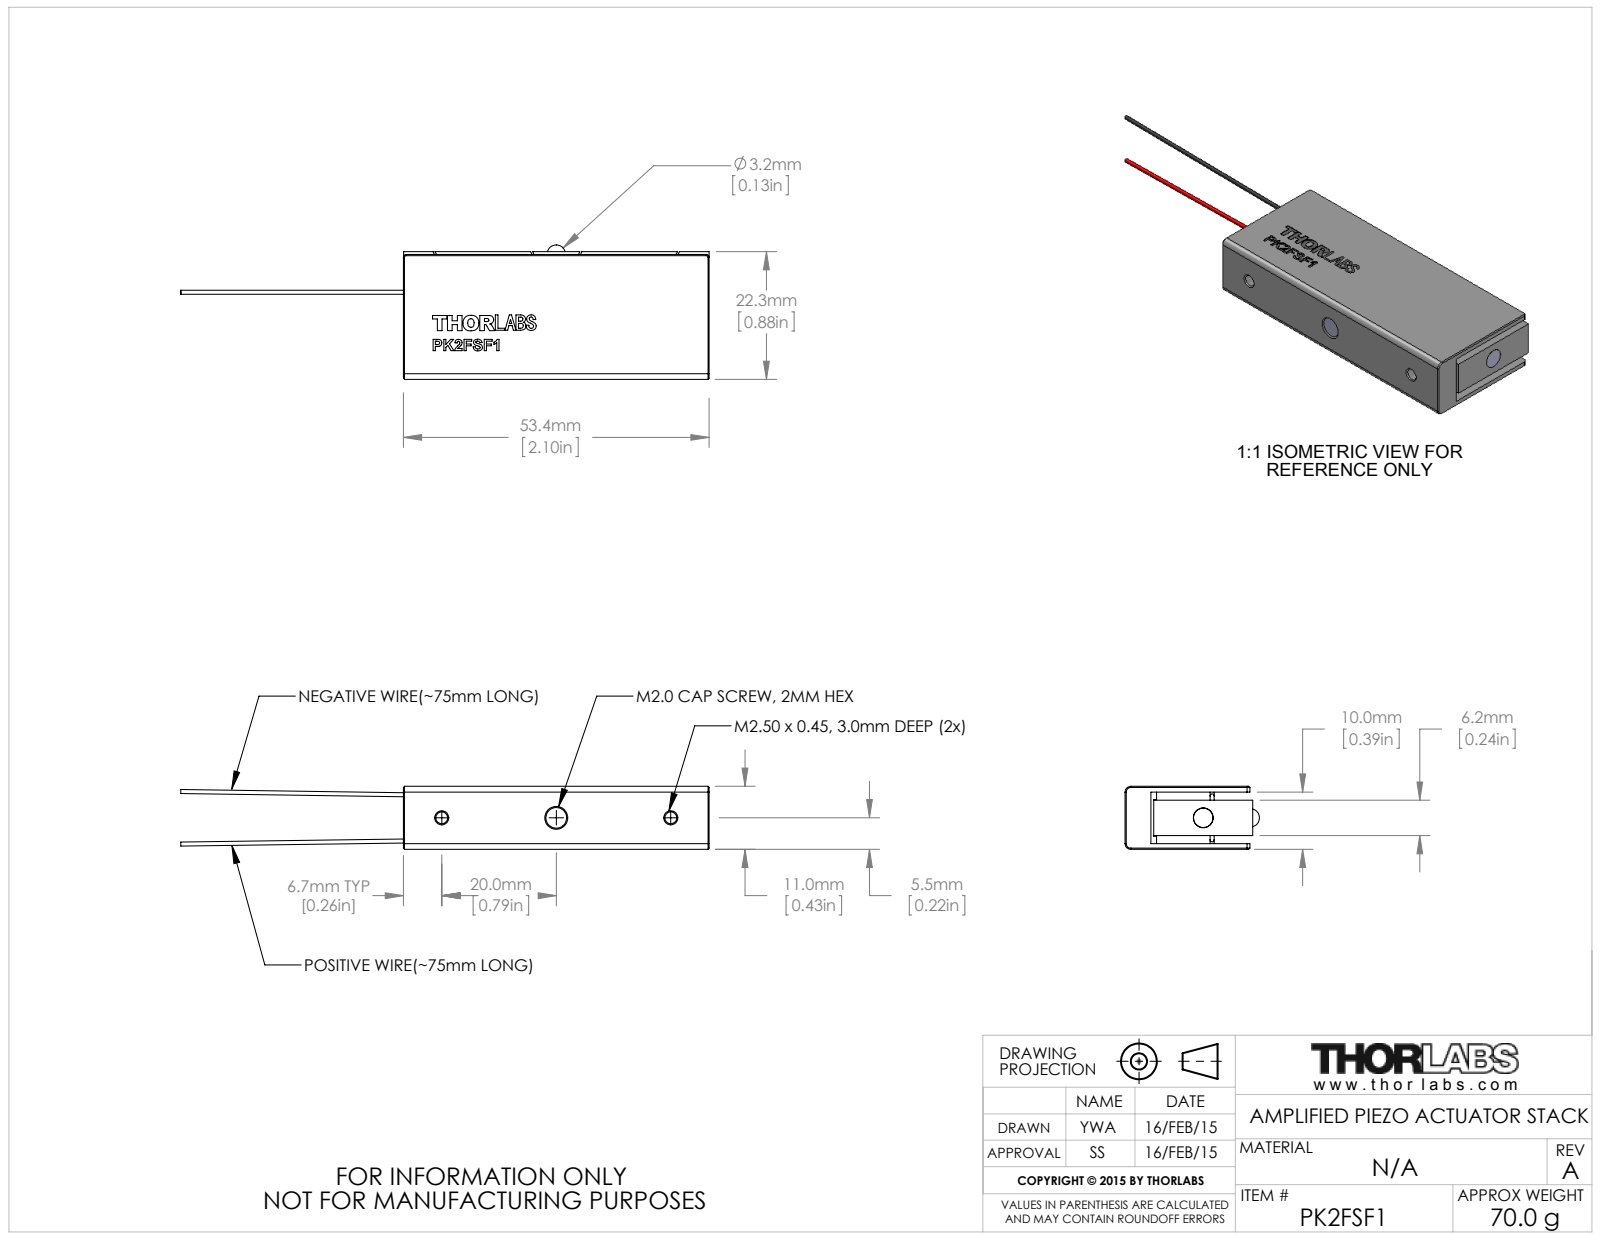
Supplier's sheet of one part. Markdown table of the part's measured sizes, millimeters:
| quantity | value |
| --- | --- |
| part name | flexure and ball--PK2FSF1; 08354; PK2FSF1; flexure cover-PK2FSF1_Default<___> (+5 more) |
| STEP written by | SolidWorks 2014 (AUTOMOTIVE_DESIGN) |
| units | millimeters |
| bodies | 11 solids, 624 faces (317 planar, 174 cylindrical, 133 other) |
| overall size | 92.27 × 23.47 × 11 |
| volume | 8 856 mm³ |
| surface area | 10 805 mm² |
| round holes (diameter × count) | 2.05 × 2, 1.78 × 1, 2.4 × 1, 3.45 × 1, 3.56 × 1, 4 × 1 |
| round bosses / shafts (diameter × count) | 1.2 × 9, 0.7 × 2, 5 × 1, 4.11 × 1, 3.6 × 1, 3.4 × 1, 1.4 × 1 |
| partial cylindrical surfaces (radius × count) | 0.15 × 48, 1.57 × 4, 0.5 × 2, 1 × 2 |
| main face-to-face distances | 10, 1, 8.58, 2.42, 1.42, 7.58, 11, 9, 6.16, 5 |
| hole center spacings | 20, 40 |
